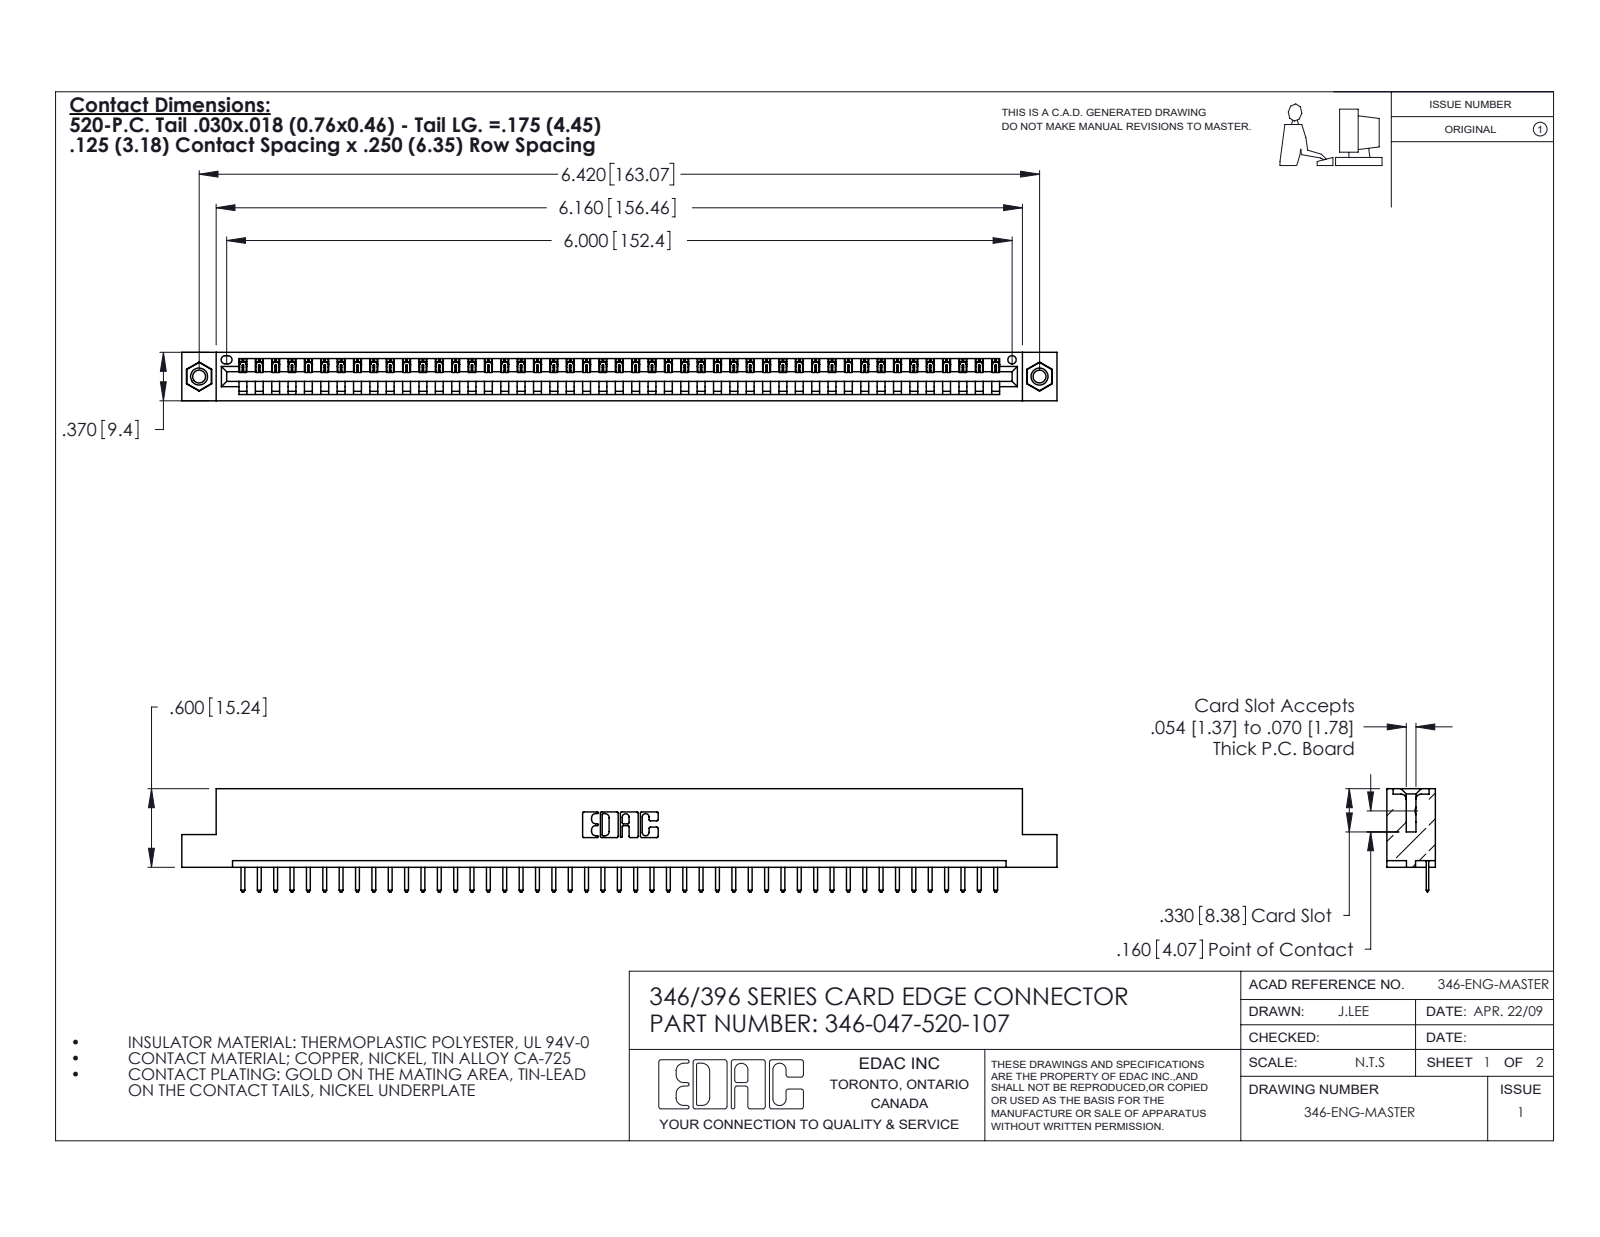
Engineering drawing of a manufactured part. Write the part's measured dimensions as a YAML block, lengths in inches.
part_name: "346 Part_Flush Mounting Lugs - 0.156 Dia-TI; 345-250-001_345-250-005-103; 346-047-520-107; 345-292-001_345-293-120"
step_written_by: "SolidWorks 2020 (CONFIG_CONTROL_DESIGN)"
units: inches
bodies: {solids: 50, faces: 3096, planar: 2082, cylindrical: 998, other: 16}
overall_size: [6.685, 0.788, 0.37]
volume: 0.985
surface_area: 30.7
round_holes:
  - {diameter: 0.098, count: 2}
  - {diameter: 0.125, count: 2}
  - {diameter: 0.156, count: 2}
  - {diameter: 0.064, count: 1}
round_bosses_or_shafts:
  - {diameter: 0.155, count: 2}
partial_cylinders:
  - {radius: 0.01, count: 96}
  - {radius: 0.006, count: 94}
  - {radius: 0.01, count: 22}
  - {radius: 0.007, count: 6}
  - {radius: 0.031, count: 6}
  - {radius: 0.026, count: 3}
  - {radius: 0.031, count: 2}
  - {radius: 0.04, count: 2}
face_to_face_distances: [0.048, 0.322, 0.37, 0.25, 0.148, 0.222, 0.1, 0.174, 0.072, 0.298]
hole_center_spacings: [0.246, 6.211, 6.42]
